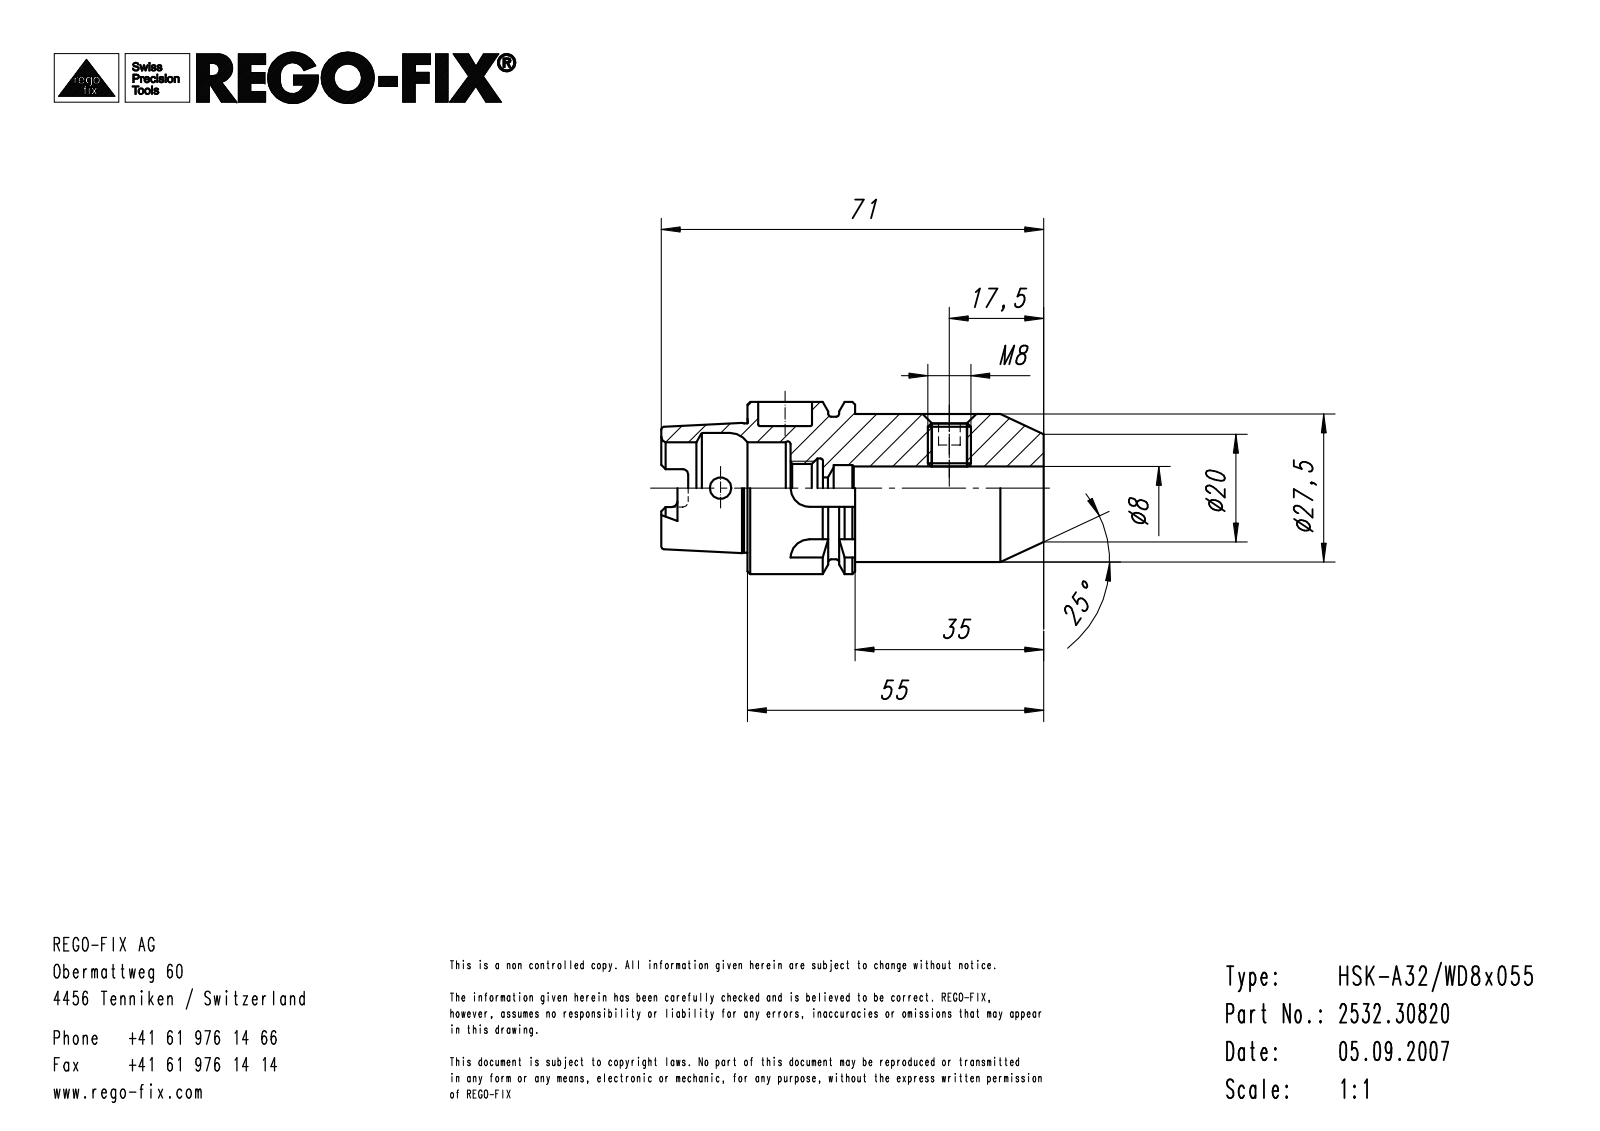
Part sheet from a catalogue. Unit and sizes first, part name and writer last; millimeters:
Units: millimetres
Overall size (bounding box): 71 × 32 × 32
Round holes (diameter × count): ⌀10 ×2, ⌀4 ×1, ⌀4.2 ×1, ⌀6.65 ×1, ⌀8 ×1, ⌀8.5 ×1, ⌀8.92 ×1, ⌀11 ×1, ⌀17 ×1, ⌀20.5 ×1
Round bosses / shafts (diameter × count): ⌀32 ×1, ⌀27.5 ×1, ⌀26.5 ×1, ⌀24.13 ×1
Partial cylindrical surfaces — rounded edges, fillets, slot ends (radius × count): R1 ×6, R1.38 ×4, R3.5 ×4
Main face-to-face distances: 55, 8, 6, 47, 20, 12, 35, 5, 1, 26
Hole centre spacings: 30.5
Volume: 31 311 mm³ · Surface area: 10 696 mm²
Bodies: 1 solid, 134 faces (52 planar, 35 cylindrical, 47 other)
STEP written by: Unknown (AUTOMOTIVE_DESIGN)
